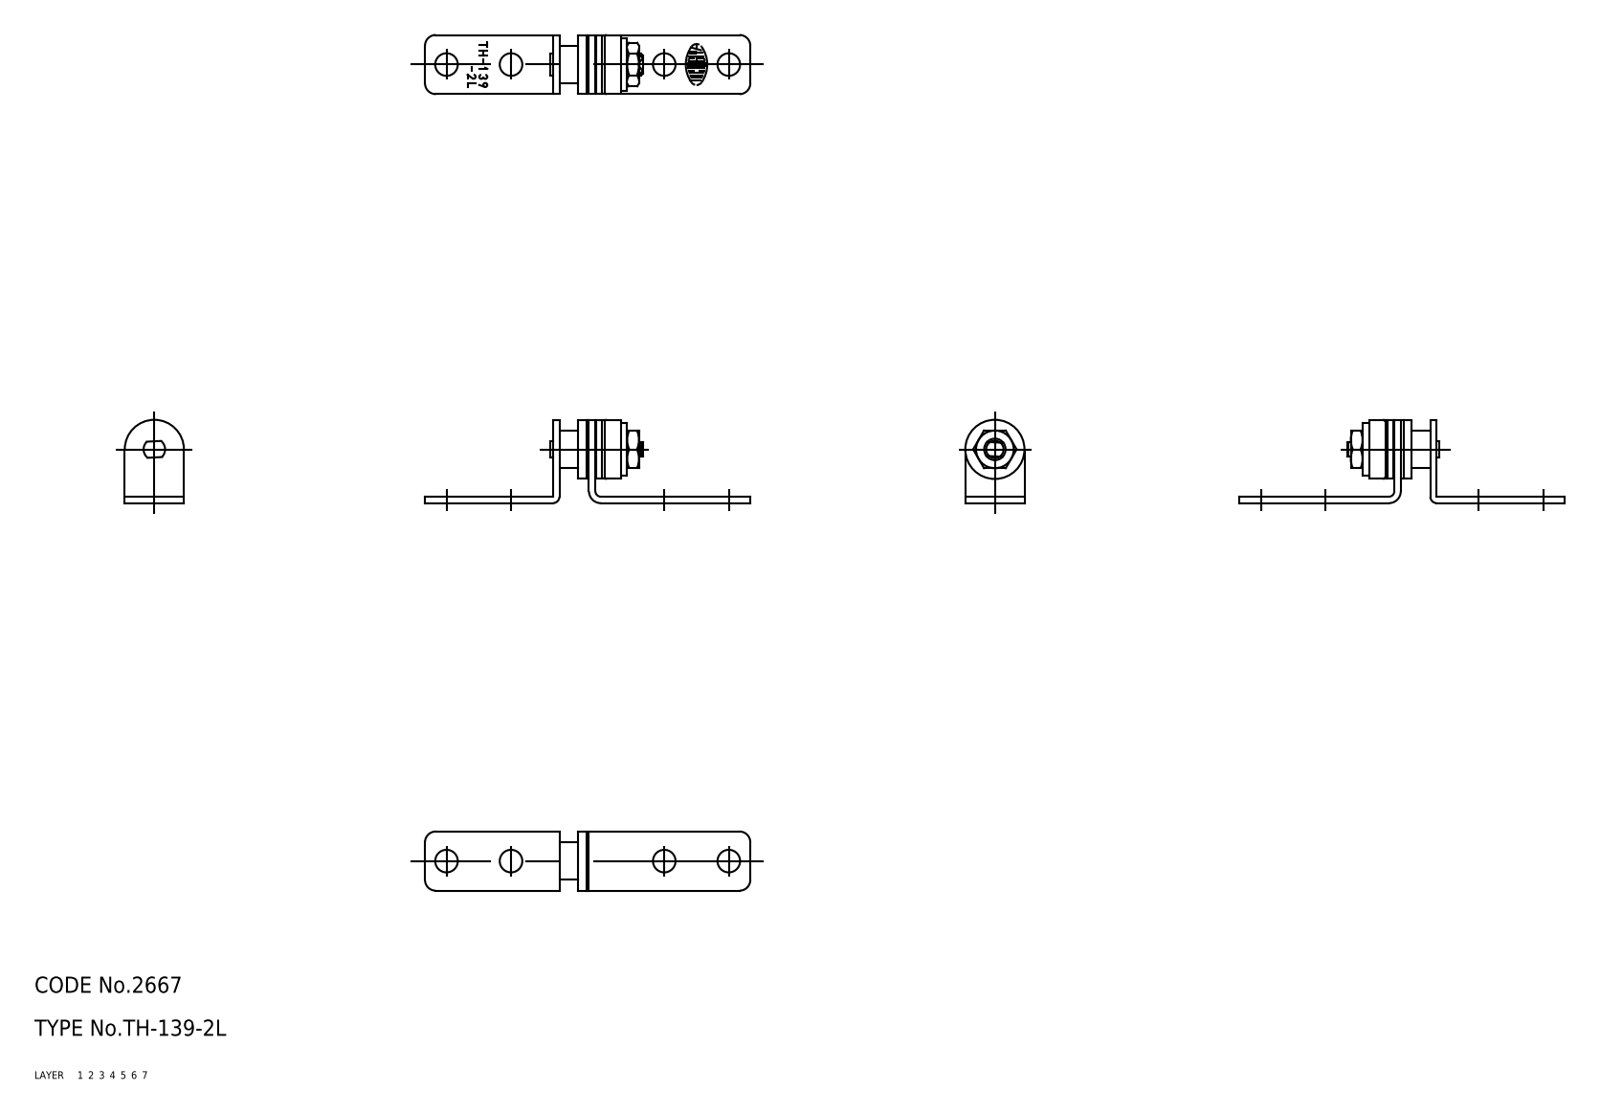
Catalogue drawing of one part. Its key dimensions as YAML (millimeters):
part_name: "67115779; 67115792; 67115805; 67115818 (+7 more)"
step_written_by: "CADfix (AUTOMOTIVE_DESIGN)"
units: millimeters
bodies: {solids: 11, faces: 121, planar: 0, cylindrical: 0, other: 121}
overall_size: [60.5, 15.77, 11.52]
volume: 1898
surface_area: 3642
